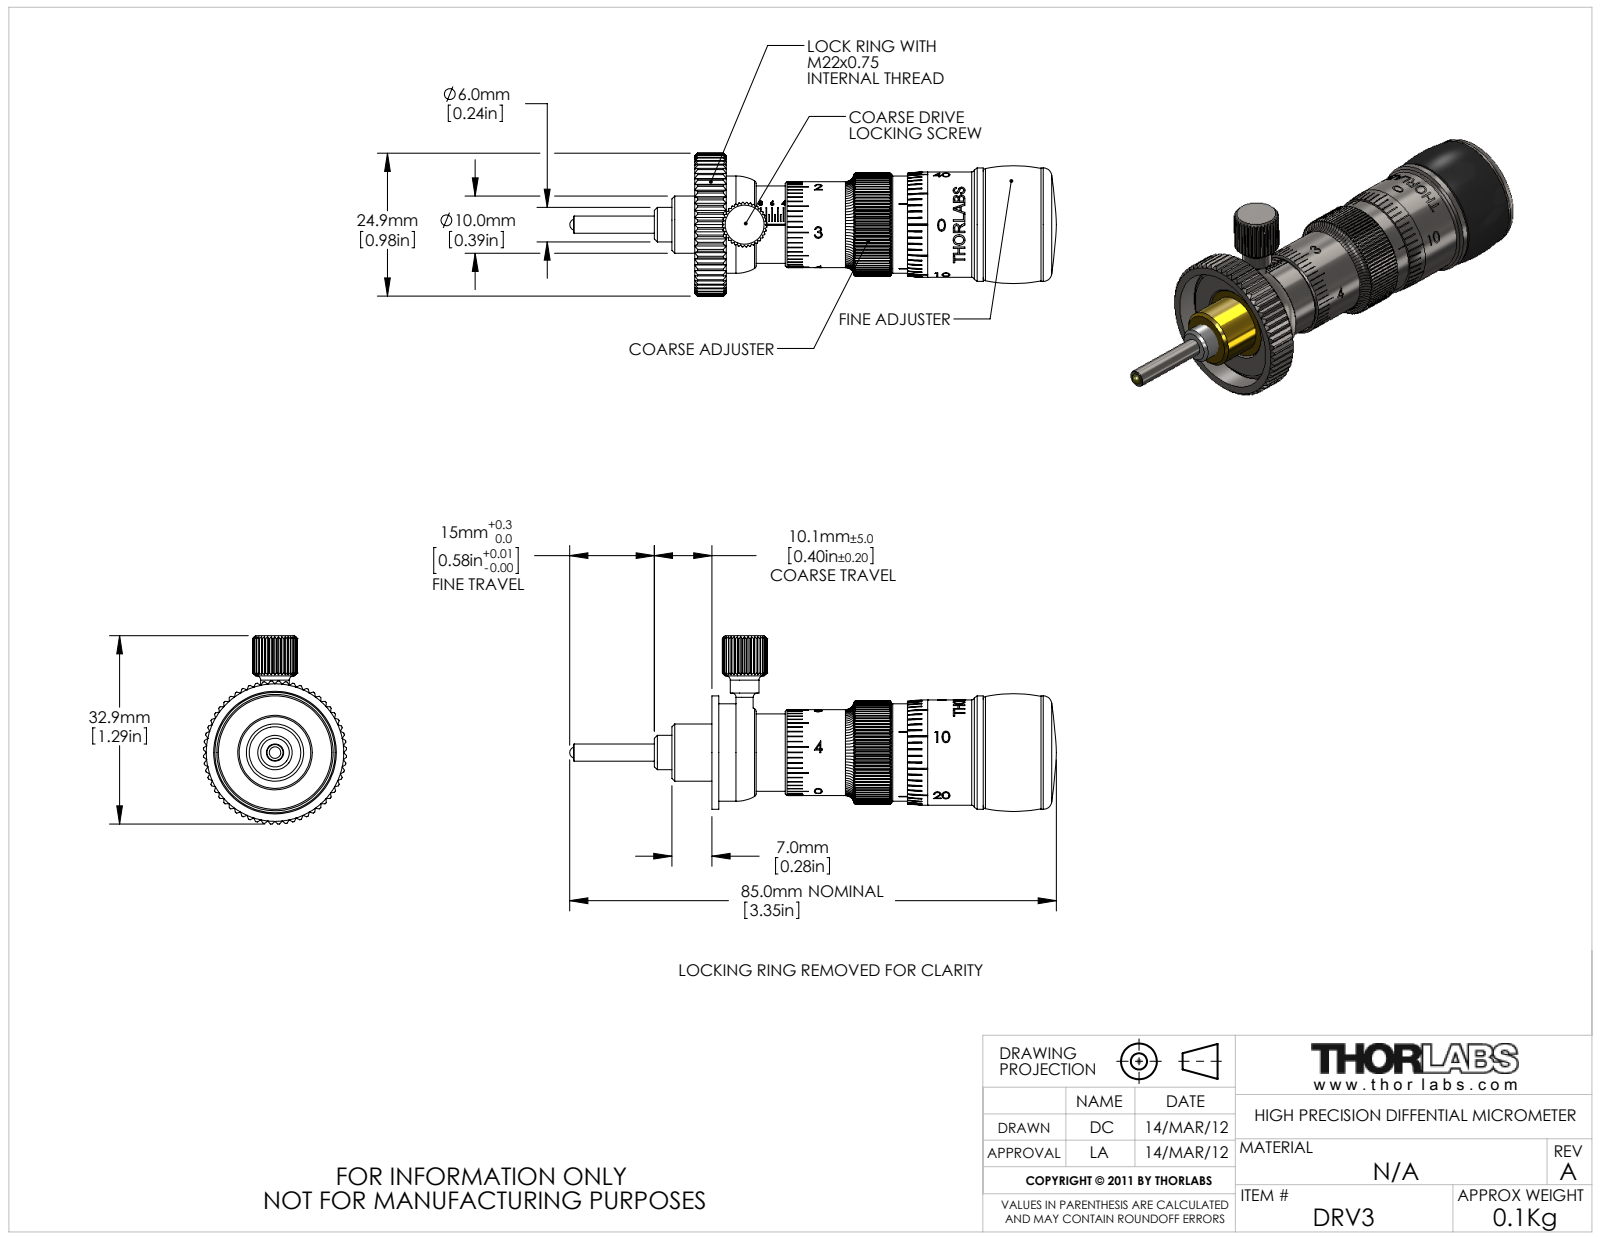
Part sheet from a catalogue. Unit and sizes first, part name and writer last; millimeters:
Units: millimetres
Overall size (bounding box): 84.98 × 32.88 × 24.98
Round holes (diameter × count): ⌀1 ×5, ⌀1.6 ×4, ⌀1.25 ×3, ⌀2.5 ×2, ⌀2 ×1, ⌀2.3 ×1, ⌀3.2 ×1, ⌀4.4 ×1, ⌀5 ×1, ⌀5.5 ×1, ⌀8.8 ×1, ⌀9 ×1
Round bosses / shafts (diameter × count): ⌀1.5 ×4, ⌀3 ×3, ⌀19.8 ×1, ⌀18.4 ×1, ⌀17 ×1, ⌀15.6 ×1, ⌀15 ×1, ⌀13.85 ×1
Partial cylindrical surfaces — rounded edges, fillets, slot ends (radius × count): R0.5 ×12, R0.1 ×8, R0.77 ×1, R1.1 ×1, R1.38 ×1, R2.05 ×1, R3.9 ×1, R6.65 ×1
Main face-to-face distances: 1.2, 2.5, 16.5, 24.57, 9.5, 1.3, 23.75, 33.25, 23.37, 22.07
Hole centre spacings: 4.1, 9.5, 9.6, 13.7, 19.1, 23.2, 26.25, 35.75
Volume: 14 049 mm³ · Surface area: 16 917 mm²
Bodies: 33 solids, 2072 faces (795 planar, 536 cylindrical, 741 other)
Part name (STEP PRODUCT): DRV3 - Coarse Scale
STEP written by: SolidWorks 2011 (AUTOMOTIVE_DESIGN)
